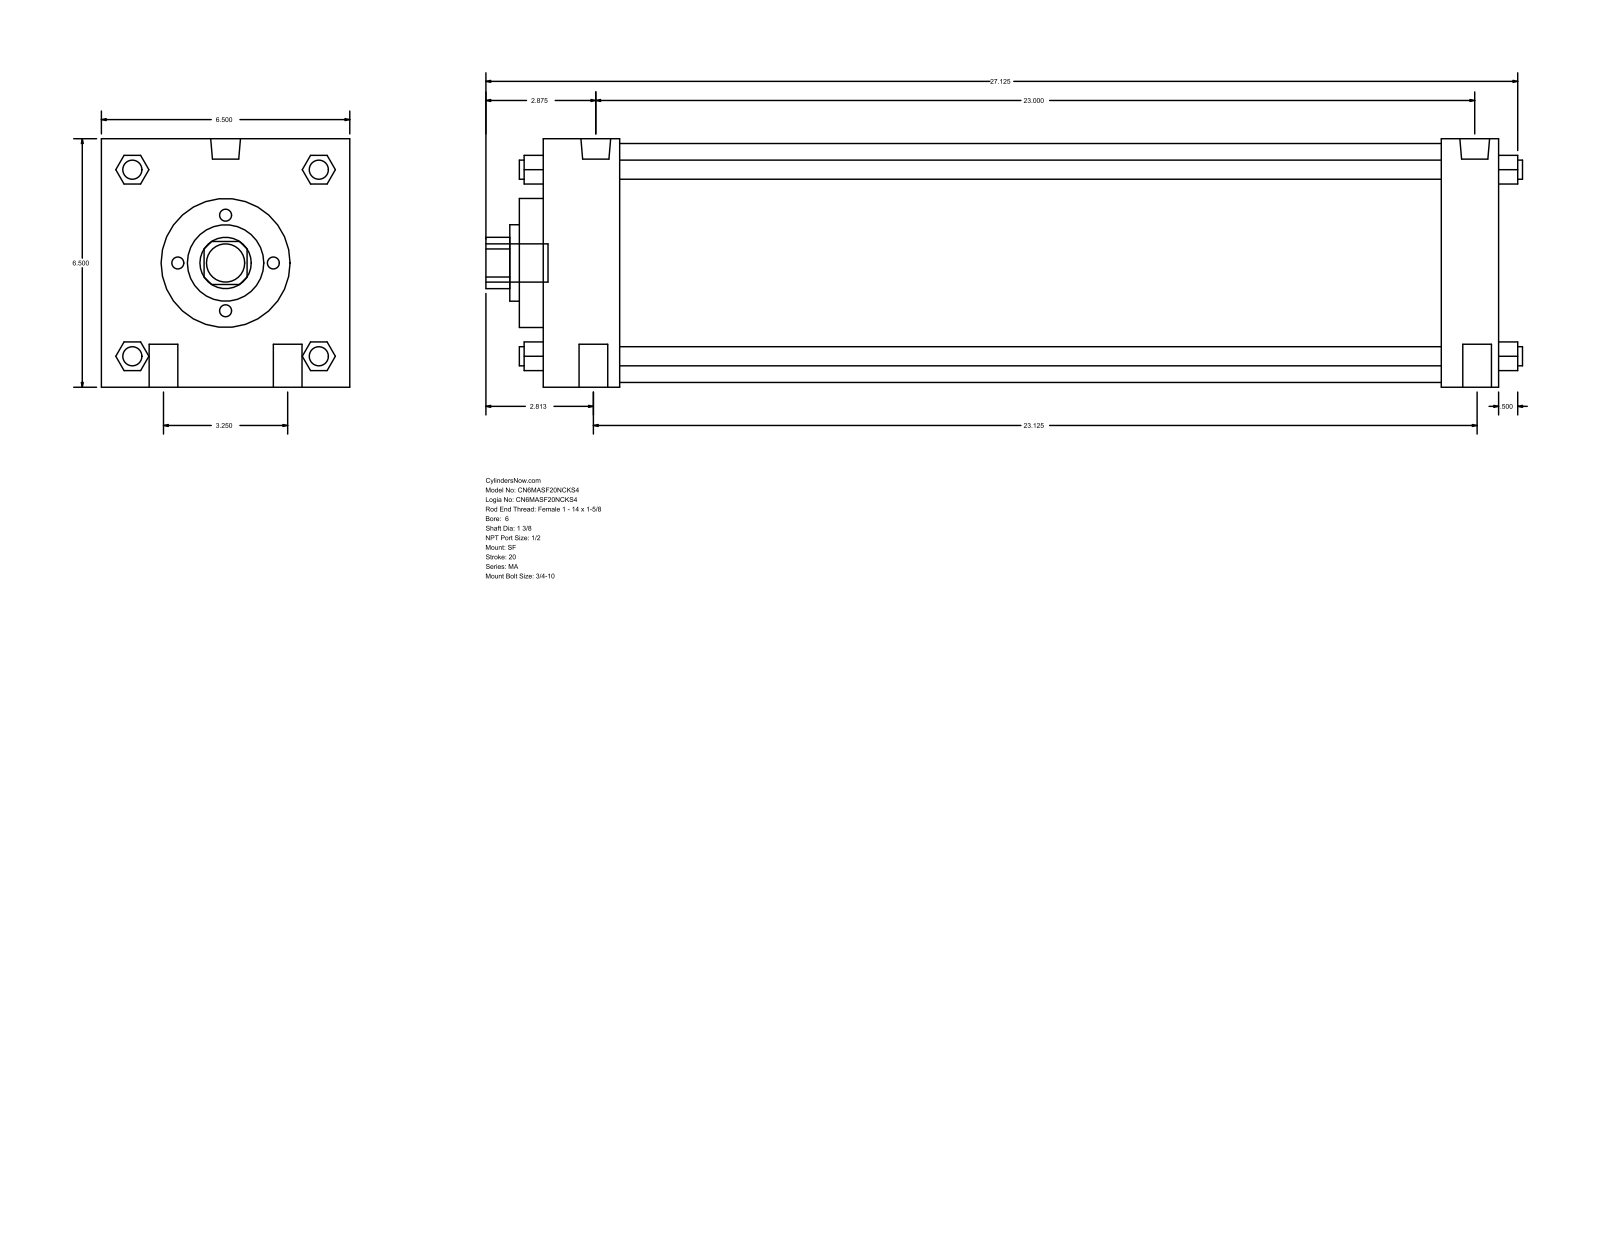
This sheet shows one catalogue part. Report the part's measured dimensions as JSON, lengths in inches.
{"part_name": "MA_SF__0600_1.375", "step_written_by": "GSSL Pune (CONFIG_CONTROL_DESIGN)", "units": "inches", "bodies": {"solids": 0, "faces": 126, "planar": 95, "cylindrical": 31, "other": 0}, "overall_size": [27.125, 6.5, 6.5], "round_holes": [[1.375, 1], [2, 1], [3.375, 1], [6.25, 1]], "round_bosses_or_shafts": [[0.75, 4], [0.5, 4], [0.778, 2], [0.687, 2], [1, 1]], "partial_cylinders_radius": [[0.672, 1]], "face_to_face_distances": [6.5, 25, 23.5, 2, 1.5, 21.5, 23, 0.625, 2.625, 24.125]}
